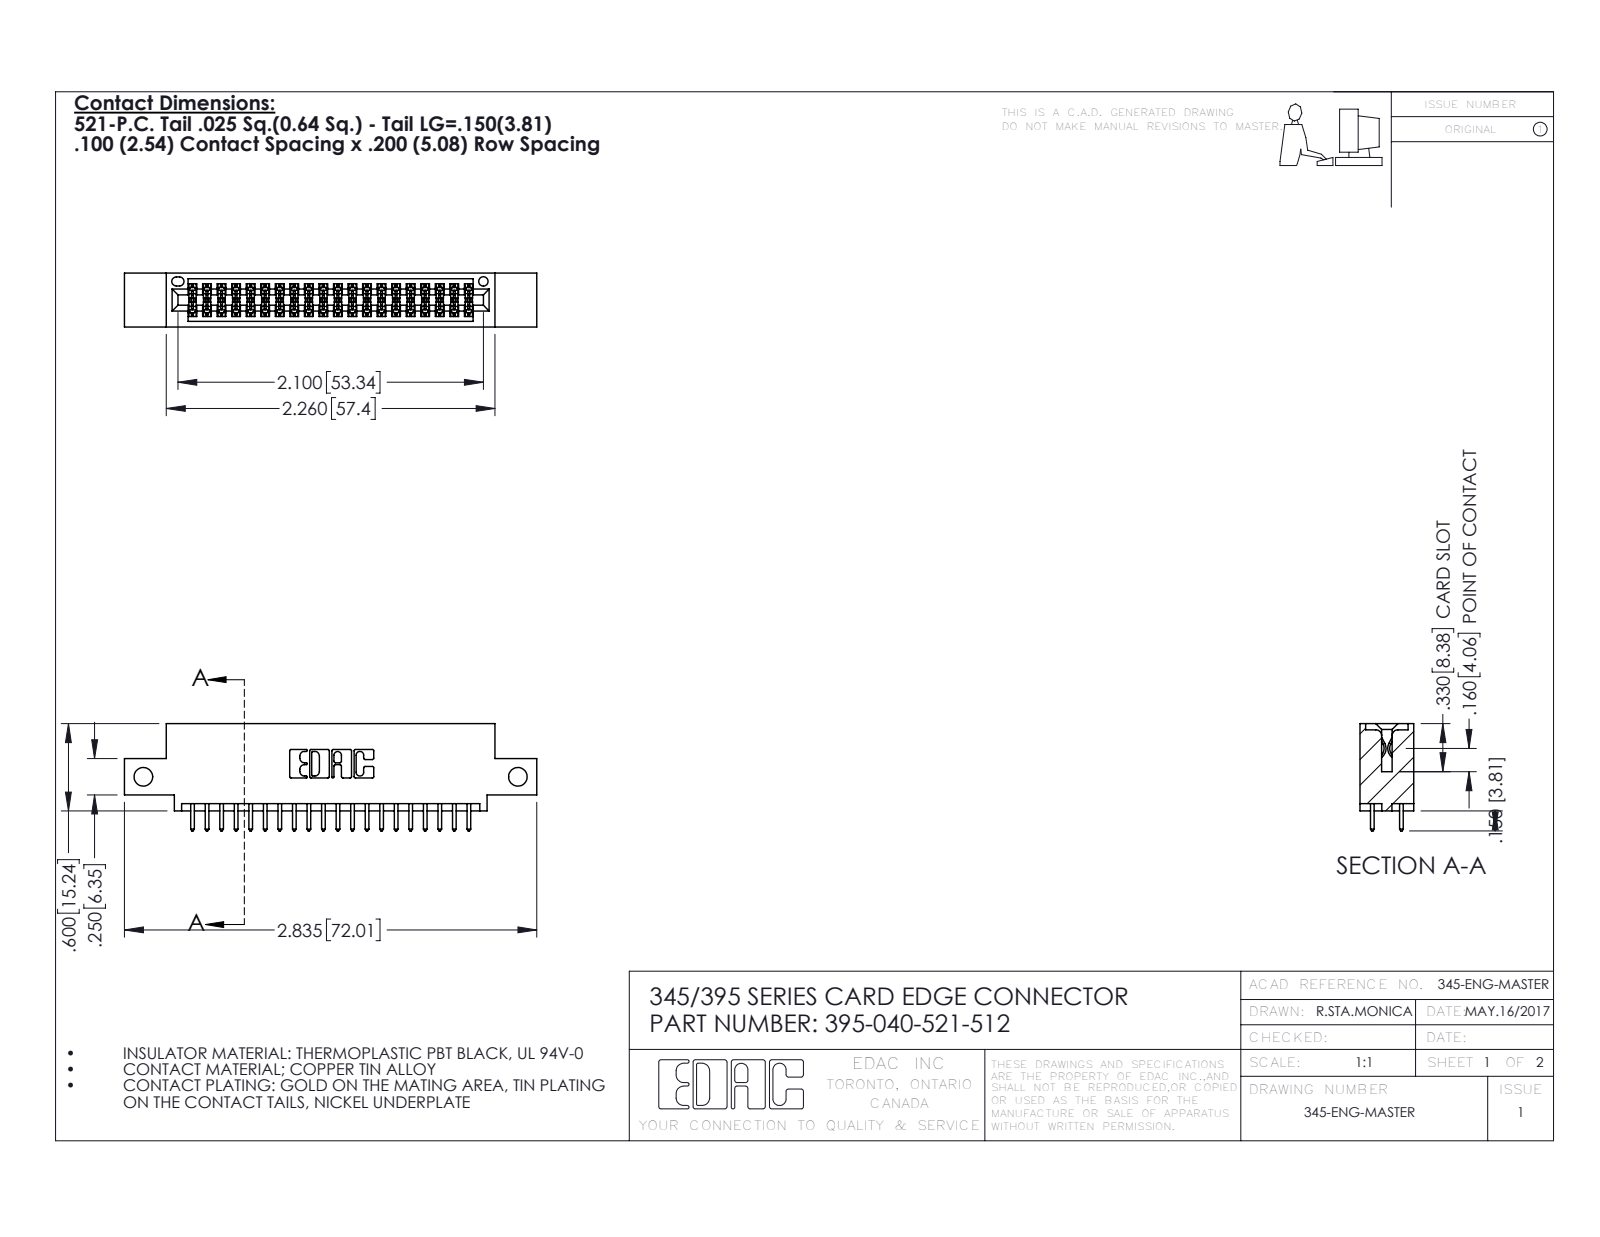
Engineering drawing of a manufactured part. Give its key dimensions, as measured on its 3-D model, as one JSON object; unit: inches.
{"part_name": "345 Part_0.110 Offset - Side Mount; 395-040-521-512; 345-292-001_345-293-121", "step_written_by": "SolidWorks 2016 (CONFIG_CONTROL_DESIGN)", "units": "inches", "bodies": {"solids": 41, "faces": 2130, "planar": 1404, "cylindrical": 726, "other": 0}, "overall_size": [2.835, 0.737, 0.37], "volume_in3": 0.404, "surface_area_in2": 14.26, "round_holes": [[0.128, 2], [0.064, 1]], "partial_cylinders_radius": [[0.006, 60], [0.01, 40], [0.01, 22], [0.007, 6], [0.031, 6], [0.026, 3], [0.014, 2], [0.019, 2]], "face_to_face_distances": [0.298, 0.072, 0.2, 0.37, 0.098, 0.272, 0.025, 0.225, 0.175, 0.149], "hole_center_spacings": [2.575]}
